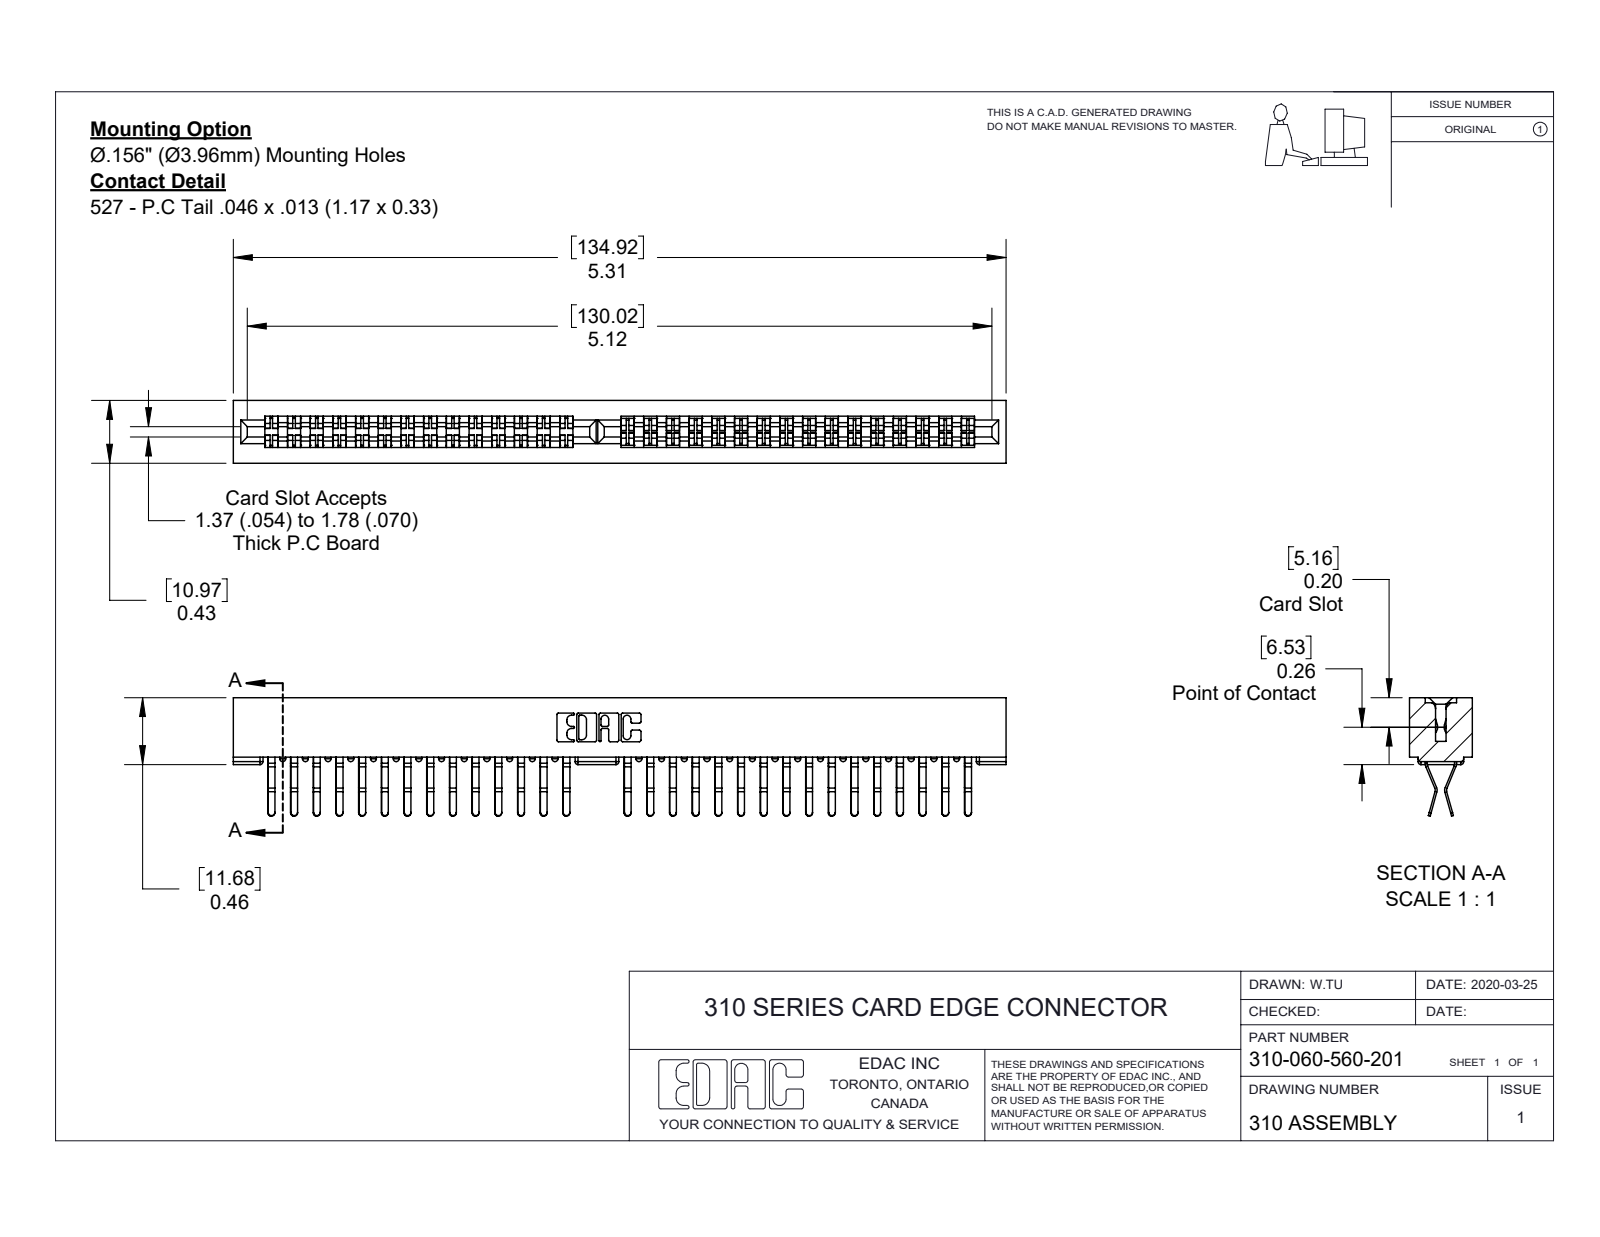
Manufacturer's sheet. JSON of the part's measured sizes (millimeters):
{"part_name": "307-290-001_560; 310 Part_No Mounting Lugs; 310-060-560-201", "step_written_by": "SolidWorks 2016 (CONFIG_CONTROL_DESIGN)", "units": "millimeters", "bodies": {"solids": 61, "faces": 3158, "planar": 2060, "cylindrical": 1034, "other": 64}, "overall_size": [134.93, 20.68, 10.97], "volume_mm3": 12085, "surface_area_mm2": 17302, "partial_cylinders_radius": [[0.51, 98], [0.58, 60], [0.25, 22], [1.27, 8], [0.17, 6], [0.8, 6], [0.3, 4], [0.64, 4]], "face_to_face_distances": [2.76, 8.22, 0.33, 10.98, 0.38, 4.75, 1.82, 5.46, 3.14, 7.84]}
